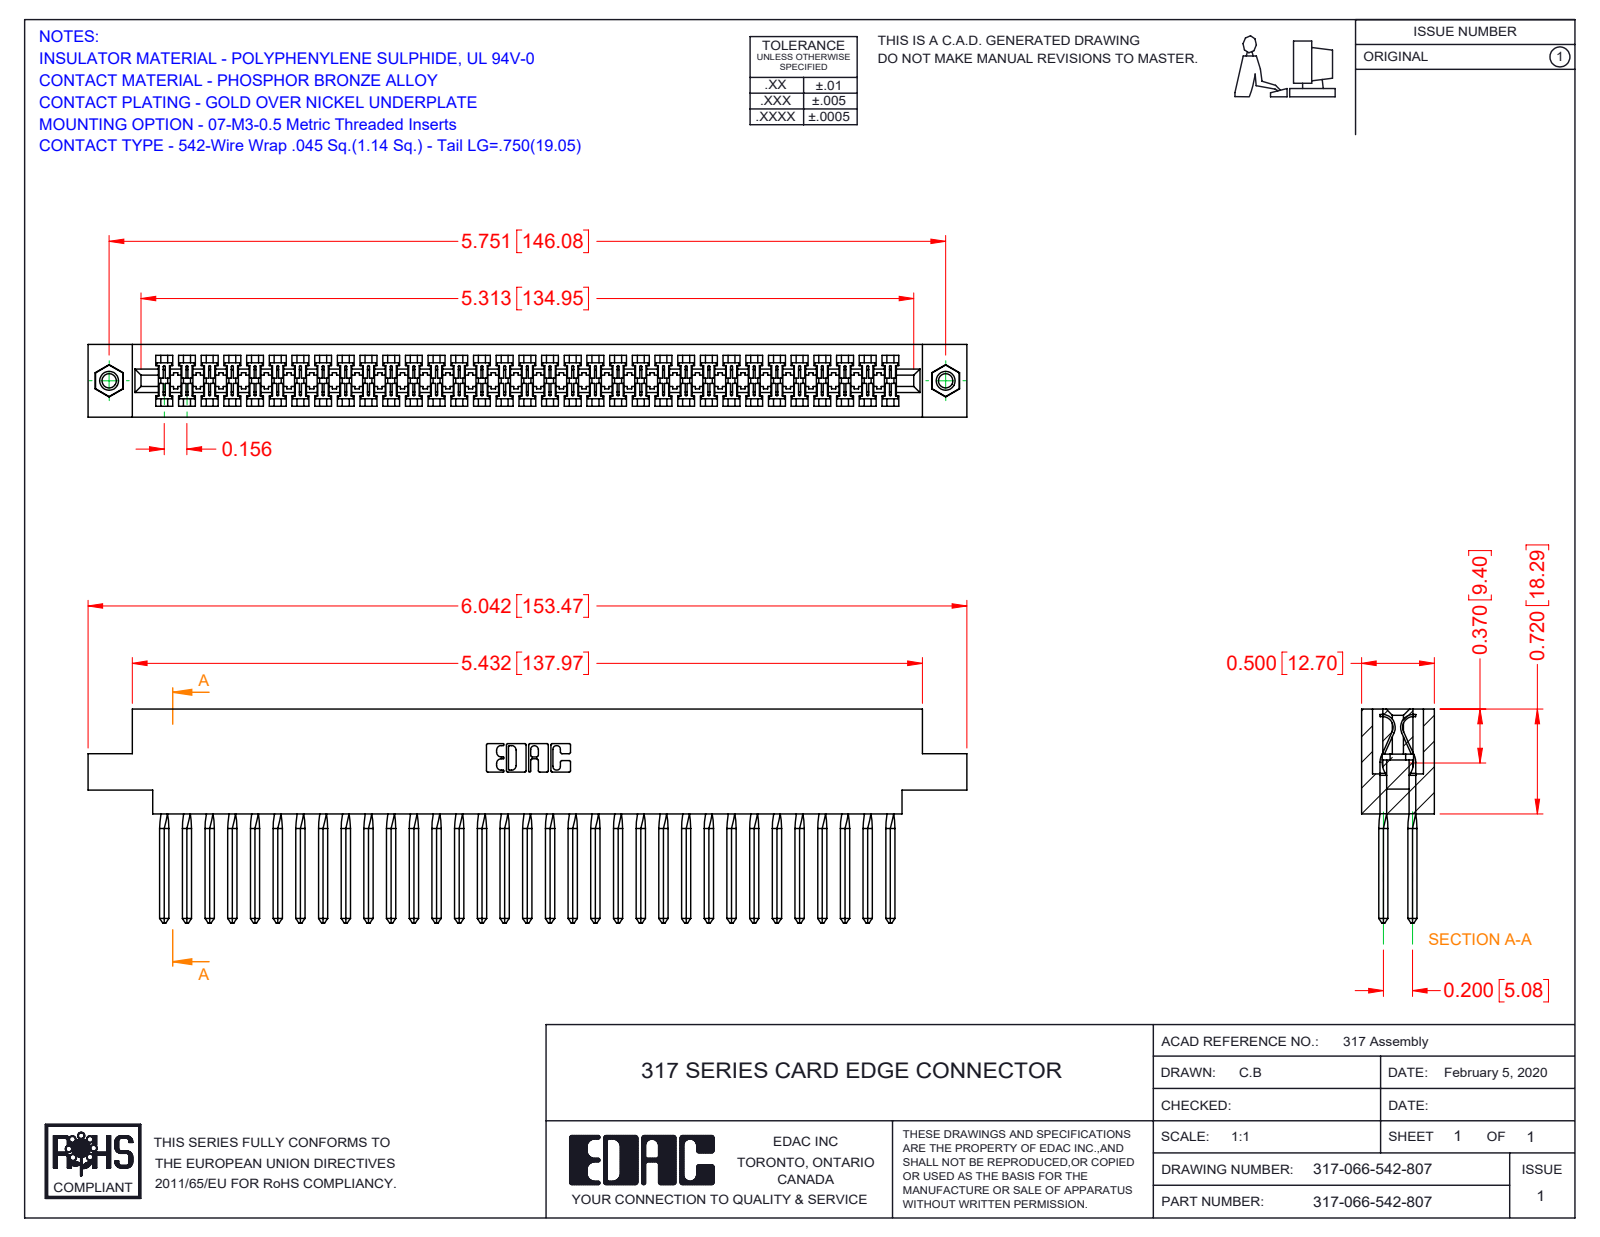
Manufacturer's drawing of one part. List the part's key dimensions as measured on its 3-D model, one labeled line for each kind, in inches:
Part name (STEP PRODUCT): 317-066-542-807; 345-250-001_345-250-005-103; 317-290-003_542; 317 Part_.156 Dia - TI
STEP written by: SolidWorks 2016 (CONFIG_CONTROL_DESIGN)
Units: inches
Bodies: 69 solids, 3924 faces (3126 planar, 518 cylindrical, 280 other)
Overall size (bounding box): 6.042 × 1.47 × 0.5
Volume: 1.515 in³ · Surface area: 53.13 in²
Round holes (diameter × count): ⌀0.098 ×2, ⌀0.125 ×2, ⌀0.156 ×2
Round bosses / shafts (diameter × count): ⌀0.155 ×2
Partial cylindrical surfaces — rounded edges, fillets, slot ends (radius × count): R0.006 ×132, R0.01 ×22, R0.007 ×6, R0.031 ×6, R0.026 ×3, R0.074 ×2, R0.089 ×2, R0.1 ×2
Main face-to-face distances: 0.5, 0.075, 0.425, 0.35, 0.2, 0.046, 0.11, 0.128, 0.372, 0.052
Hole centre spacings: 5.751
